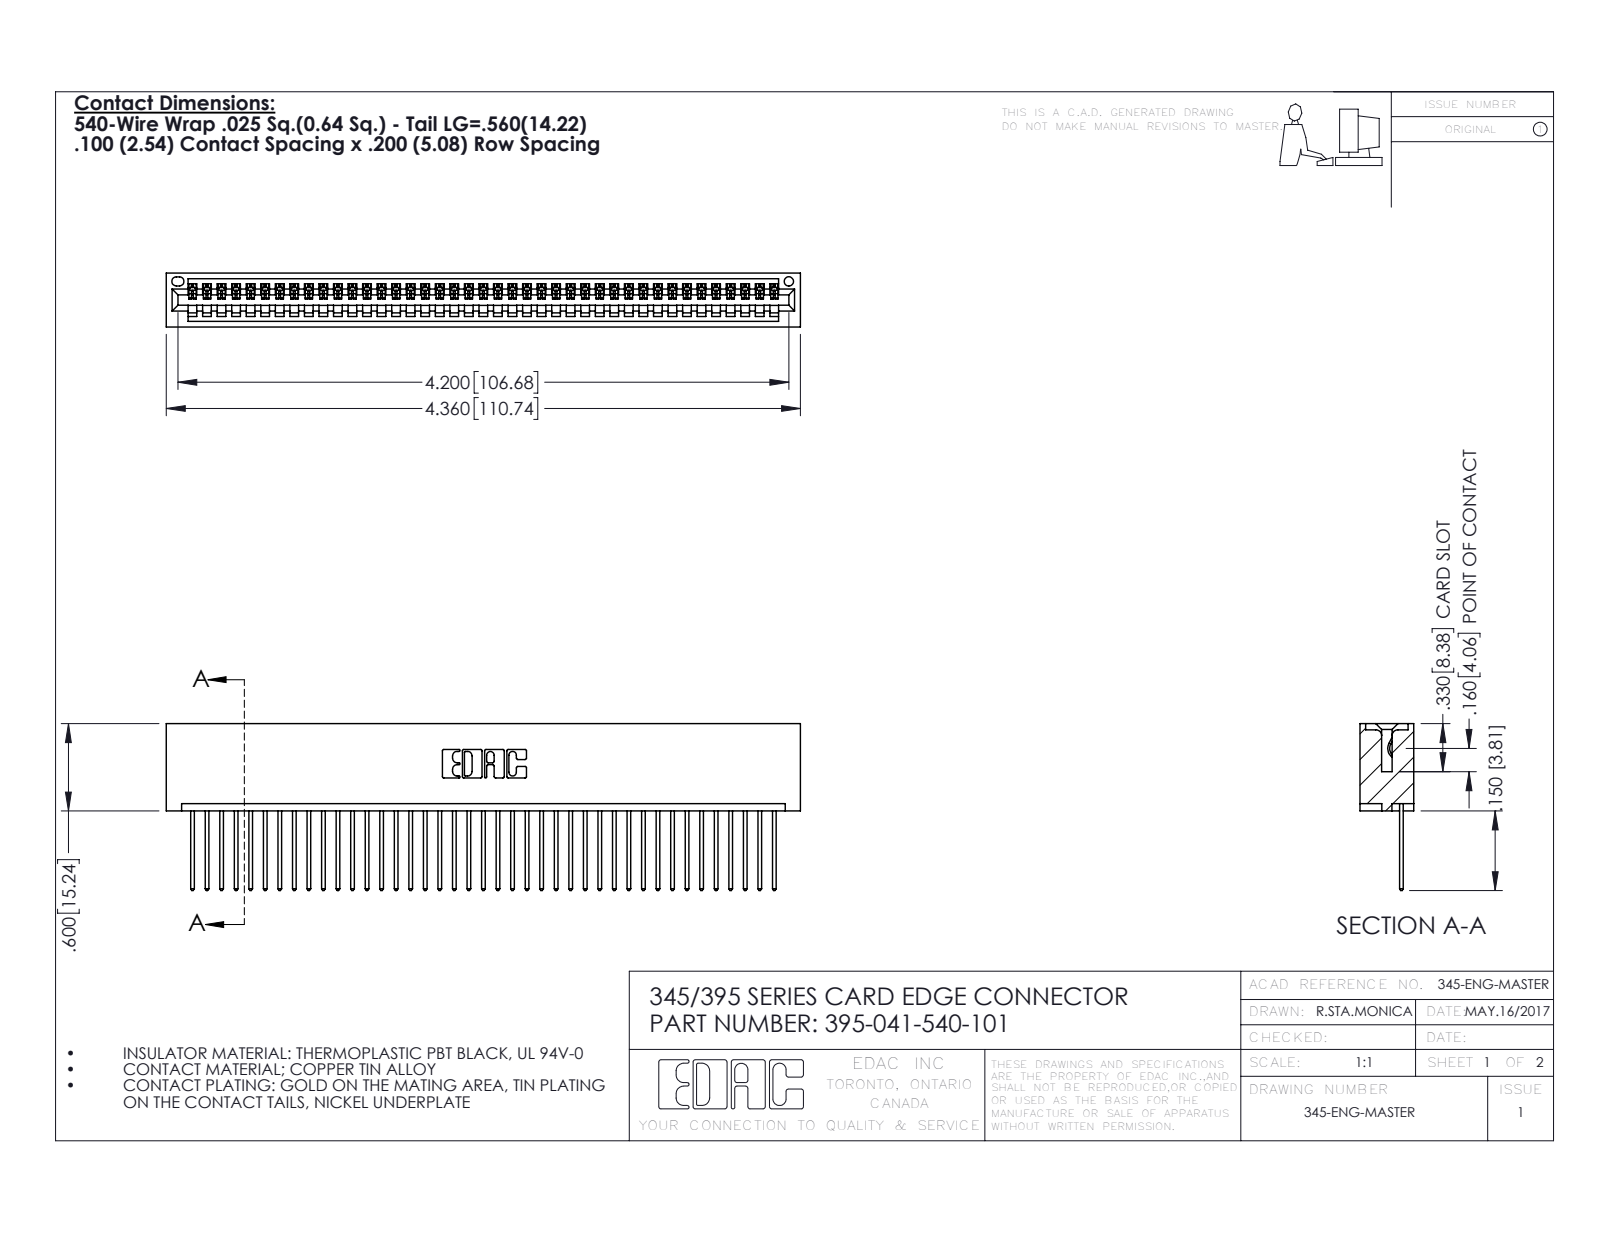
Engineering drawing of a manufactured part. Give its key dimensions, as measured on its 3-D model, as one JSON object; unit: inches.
{"part_name": "395-041-540-101; 345-292-001_345-293-140; 345 Part_No Mounting Lugs", "step_written_by": "SolidWorks 2016 (CONFIG_CONTROL_DESIGN)", "units": "inches", "bodies": {"solids": 42, "faces": 2496, "planar": 1716, "cylindrical": 780, "other": 0}, "overall_size": [4.36, 1.147, 0.37], "volume_in3": 0.68, "surface_area_in2": 23.86, "round_holes": [[0.064, 1]], "partial_cylinders_radius": [[0.006, 82], [0.01, 82], [0.01, 22], [0.007, 6], [0.031, 6], [0.026, 3], [0.031, 2], [0.04, 2]], "face_to_face_distances": [0.072, 0.298, 0.098, 0.272, 0.025, 0.37, 0.2, 0.225, 0.149, 0.072]}
